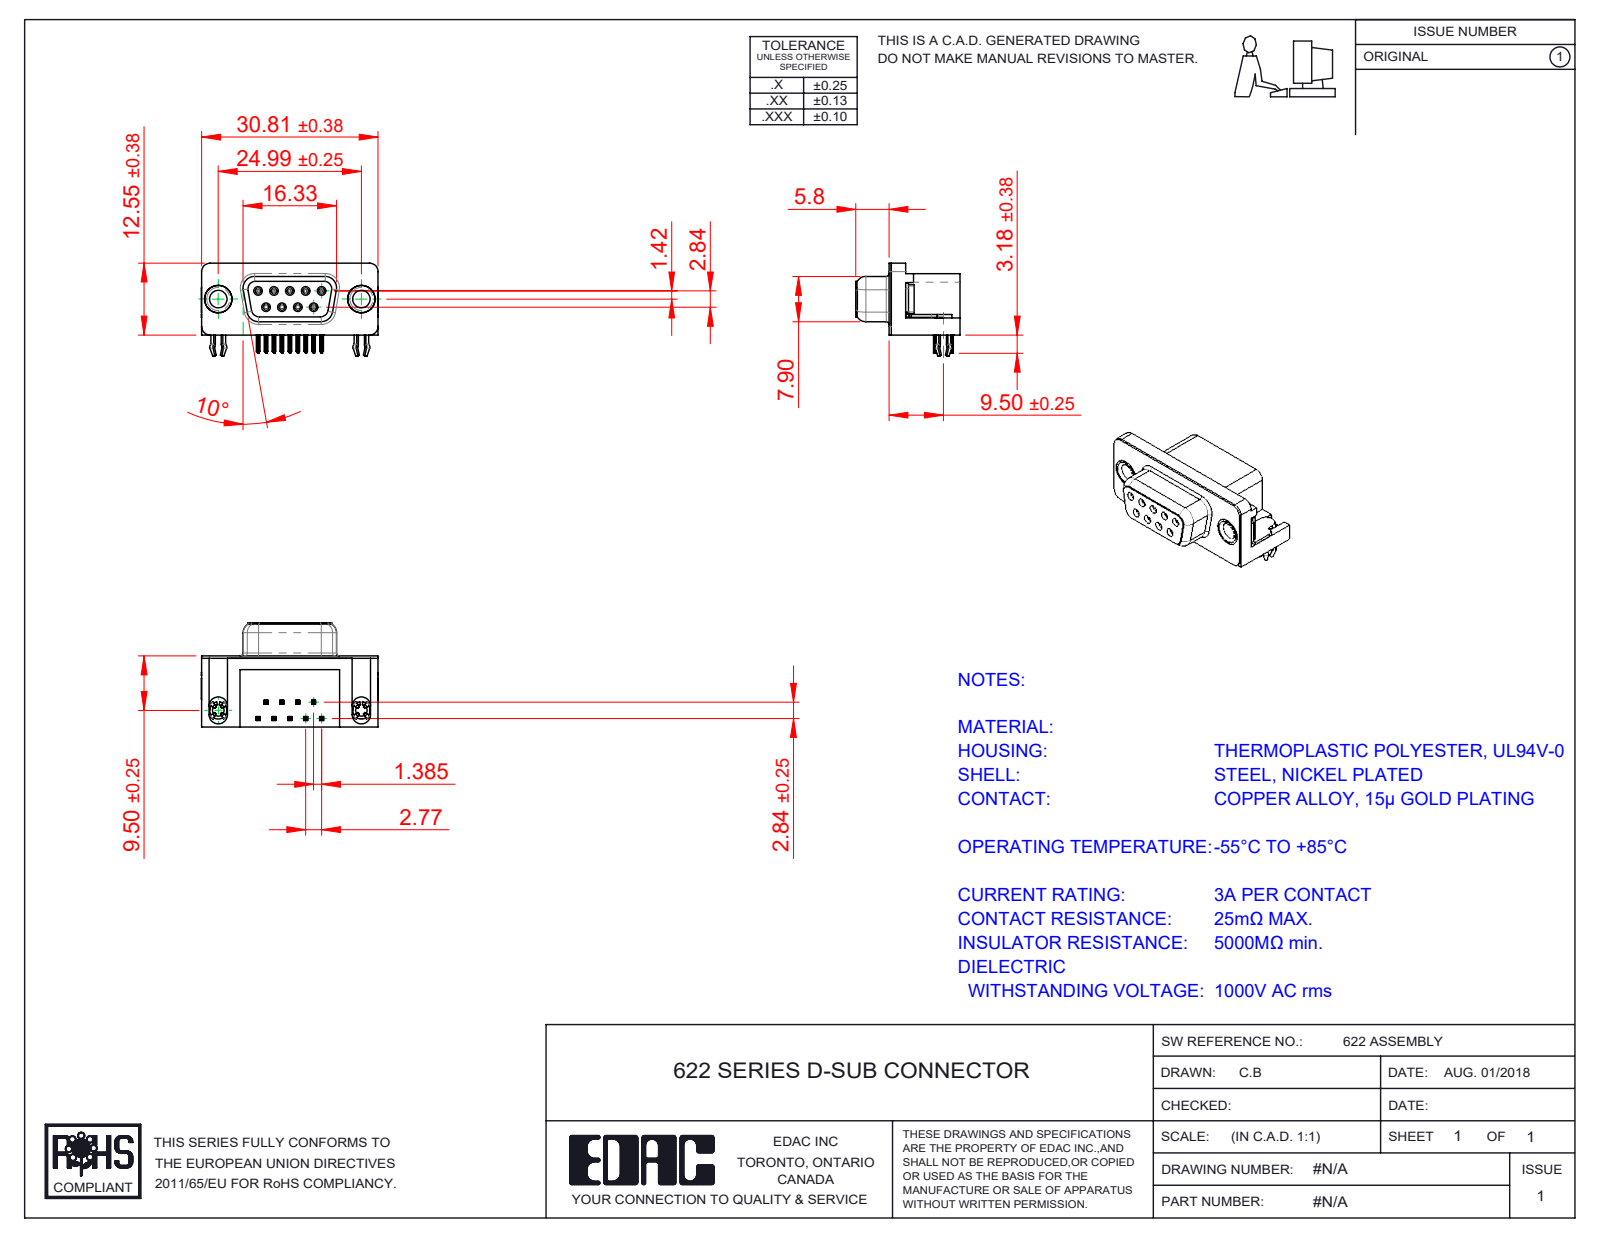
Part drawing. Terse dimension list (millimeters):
name: 622 Thru Hole Rivet; 622-009-360-051; 622 Socket Bottom; 622 Shell_9 Socket (+3 more)
written by: SolidWorks 2016 (CONFIG_CONTROL_DESIGN)
unit: mm
bodies: 15 solids, 1562 faces (684 planar, 410 cylindrical, 468 other)
size: 30.89 × 18.2 × 15.73
volume: 3 725 mm³; area: 5 129 mm²
holes: 9× ⌀0.8, 9× ⌀0.9, 2× ⌀2.26, 2× ⌀3.05, 2× ⌀4, 2× ⌀4.8, 2× ⌀5
bosses: 9× ⌀1.2, 2× ⌀4.9, 2× ⌀4.75, 2× ⌀3.85, 2× ⌀3.26
rounds: 72× R0.1, 36× R0.15, 18× R0.35, 18× R1, 9× R0.34, 8× R0.25, 8× R1.35, 8× R1.6
face distances: 0.4, 12, 12.4, 0.35, 2.9, 2.5, 6.2, 10.34, 9.5, 5.8
hole spacings: 3.16, 2.77, 5.54, 5.03, 5.04, 8.31, 7.48, 7.49
